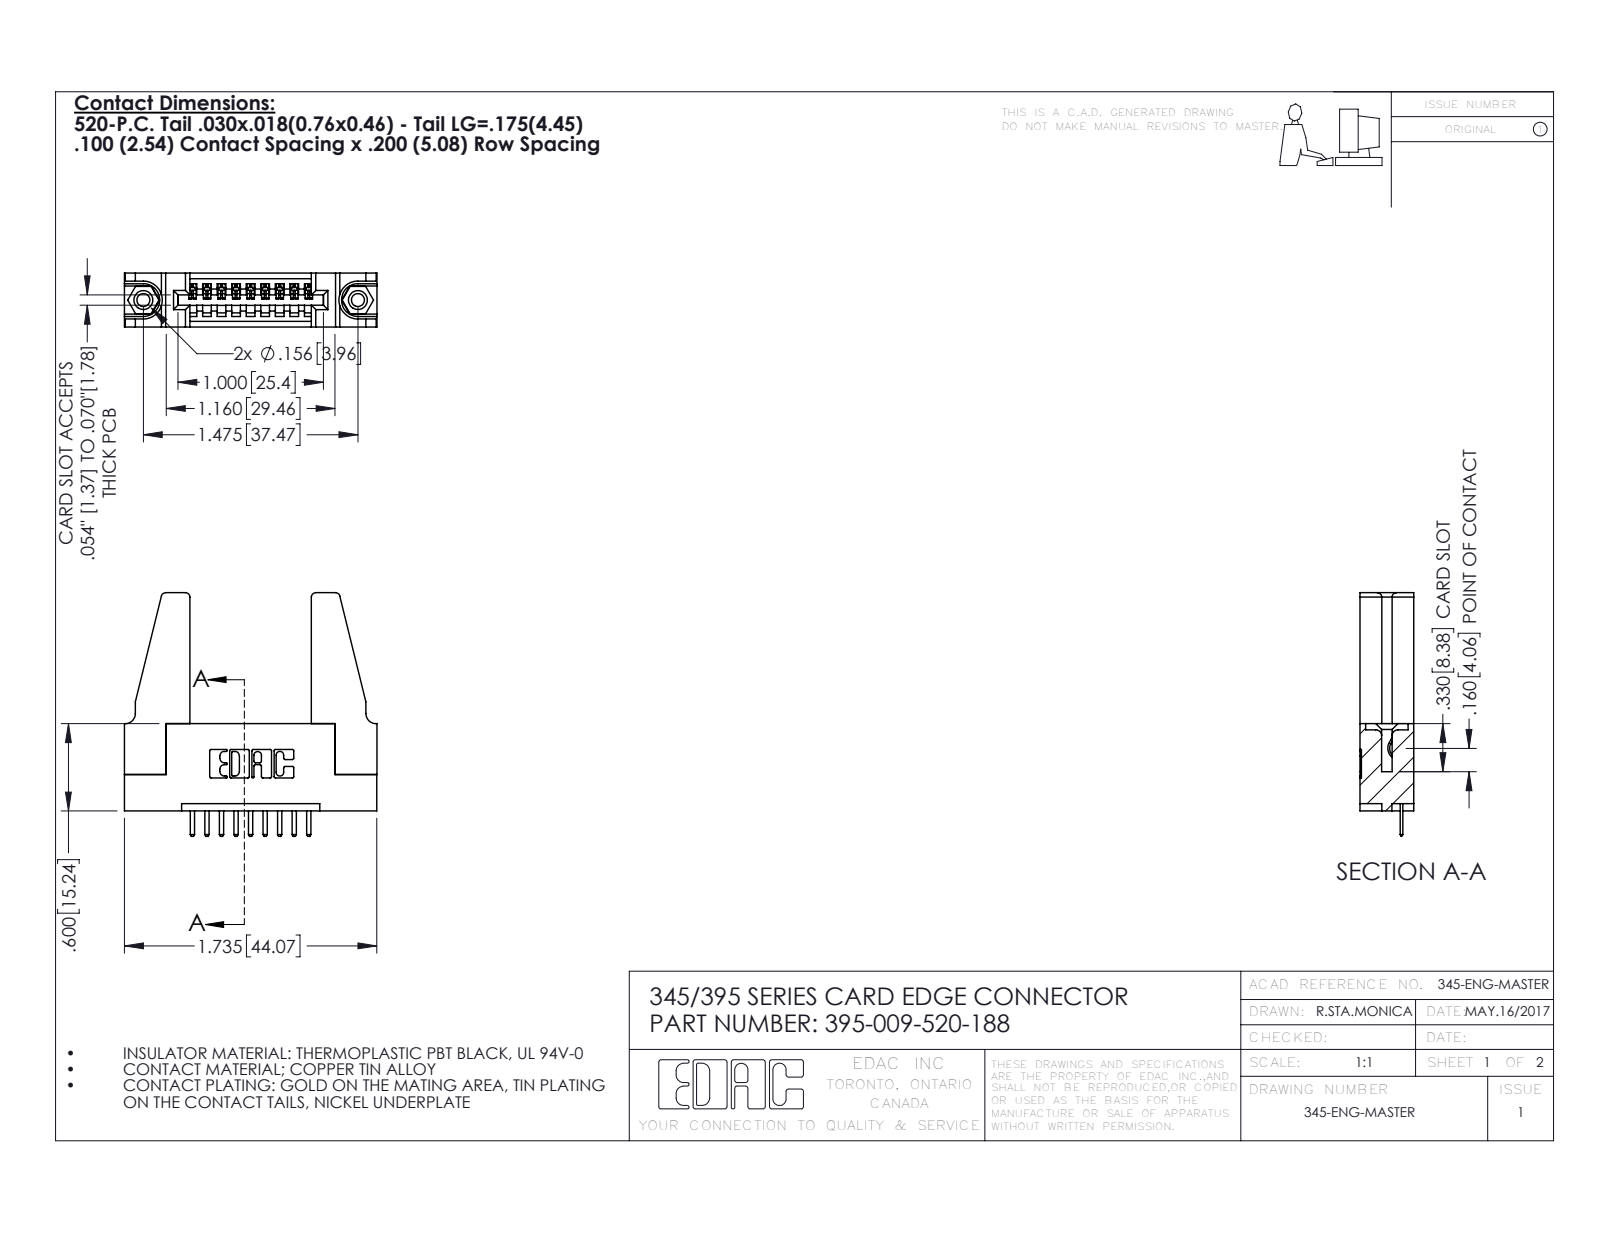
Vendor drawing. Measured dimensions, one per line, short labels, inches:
name: 395-009-520-188; 345-292-001_345-293-120; 345-220-078_345-220-088; 345-250-001_345-250-001-102 (+1 more)
written by: SolidWorks 2016 (CONFIG_CONTROL_DESIGN)
unit: in
bodies: 14 solids, 808 faces (530 planar, 262 cylindrical, 16 other)
size: 1.736 × 1.675 × 0.37
volume: 0.436 in³; area: 12.04 in²
holes: 2× ⌀0.089, 2× ⌀0.125, 2× ⌀0.156, 1× ⌀0.064
bosses: 2× ⌀0.155
rounds: 22× R0.01, 20× R0.01, 18× R0.006, 8× R0.03, 6× R0.007, 6× R0.031, 3× R0.026, 2× R0.031
face distances: 0.37, 0.072, 0.298, 0.2, 0.098, 0.272, 0.025, 0.15, 0.148, 0.25
hole spacings: 0.27, 1.244, 1.475
